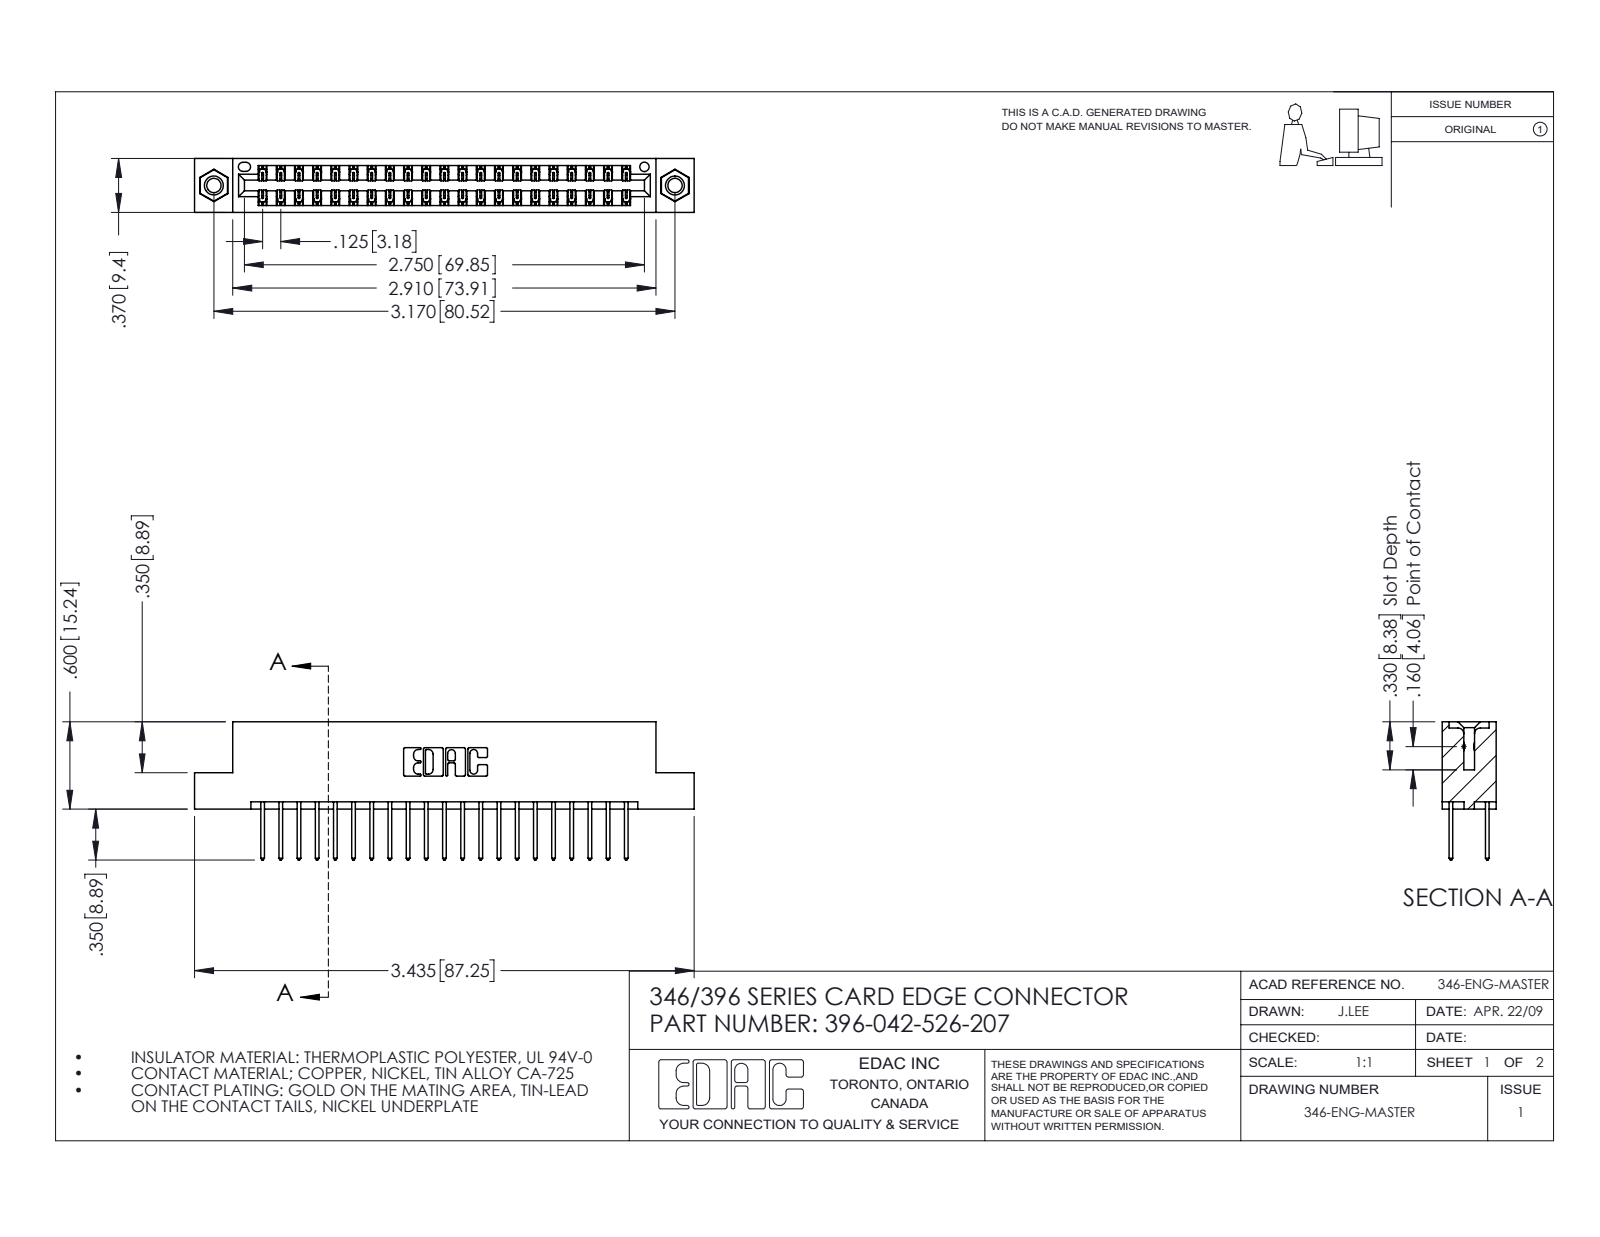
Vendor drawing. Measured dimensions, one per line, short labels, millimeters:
name: 345-250-001_345-250-005-103; 396-042-526-207; 345-292-001_345-293-126; 346 Part_Flush Mounting Lugs - 0.156 Dia-TI
written by: SolidWorks 2016 (CONFIG_CONTROL_DESIGN)
unit: mm
bodies: 45 solids, 2366 faces (1578 planar, 772 cylindrical, 16 other)
size: 87.2 × 24.1 × 9.4
volume: 8 410 mm³; area: 11 560 mm²
holes: 2× ⌀2.5, 2× ⌀3.2, 2× ⌀4, 1× ⌀1.6
bosses: 2× ⌀3.9
rounds: 63× R0.2, 42× R0.3, 22× R0.3, 6× R0.2, 6× R0.8, 3× R0.7, 2× R0.4, 2× R0.6
face distances: 1.2, 8.2, 6.4, 9.4, 1.8, 7.6, 0.6, 7, 3.8, 5.6
hole spacings: 6.2, 75.3, 80.5
